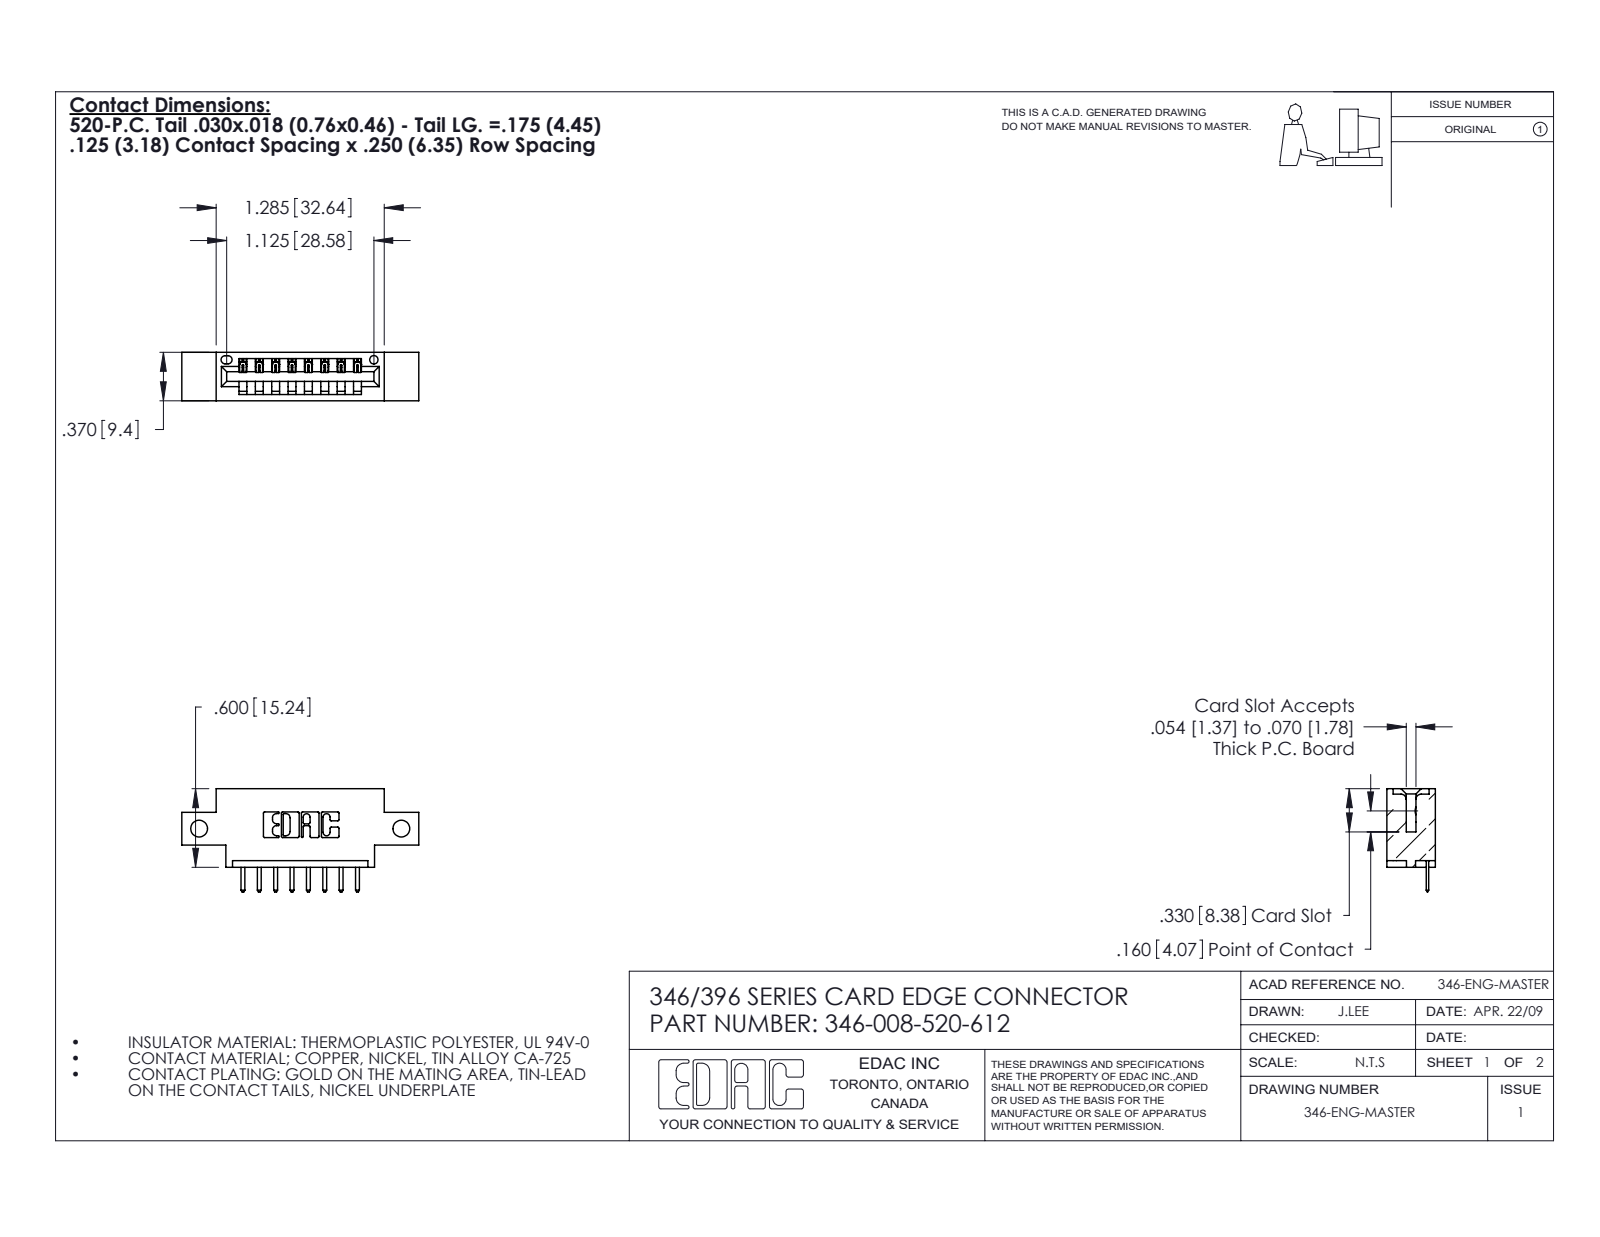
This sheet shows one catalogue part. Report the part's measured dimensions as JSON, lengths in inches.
{"part_name": "346 Part_0.170 Offset - Side Mount; 346-008-520-612; 345-292-001_345-293-120", "step_written_by": "SolidWorks 2020 (CONFIG_CONTROL_DESIGN)", "units": "inches", "bodies": {"solids": 9, "faces": 622, "planar": 416, "cylindrical": 206, "other": 0}, "overall_size": [1.81, 0.788, 0.37], "volume_in3": 0.238, "surface_area_in2": 6.893, "round_holes": [[0.128, 2], [0.064, 1]], "partial_cylinders_radius": [[0.01, 22], [0.01, 18], [0.006, 16], [0.007, 6], [0.031, 6], [0.026, 3], [0.031, 2], [0.04, 2]], "face_to_face_distances": [0.25, 0.37, 0.048, 0.322, 0.148, 0.222, 0.1, 0.174, 0.5, 0.185], "hole_center_spacings": [1.545]}
